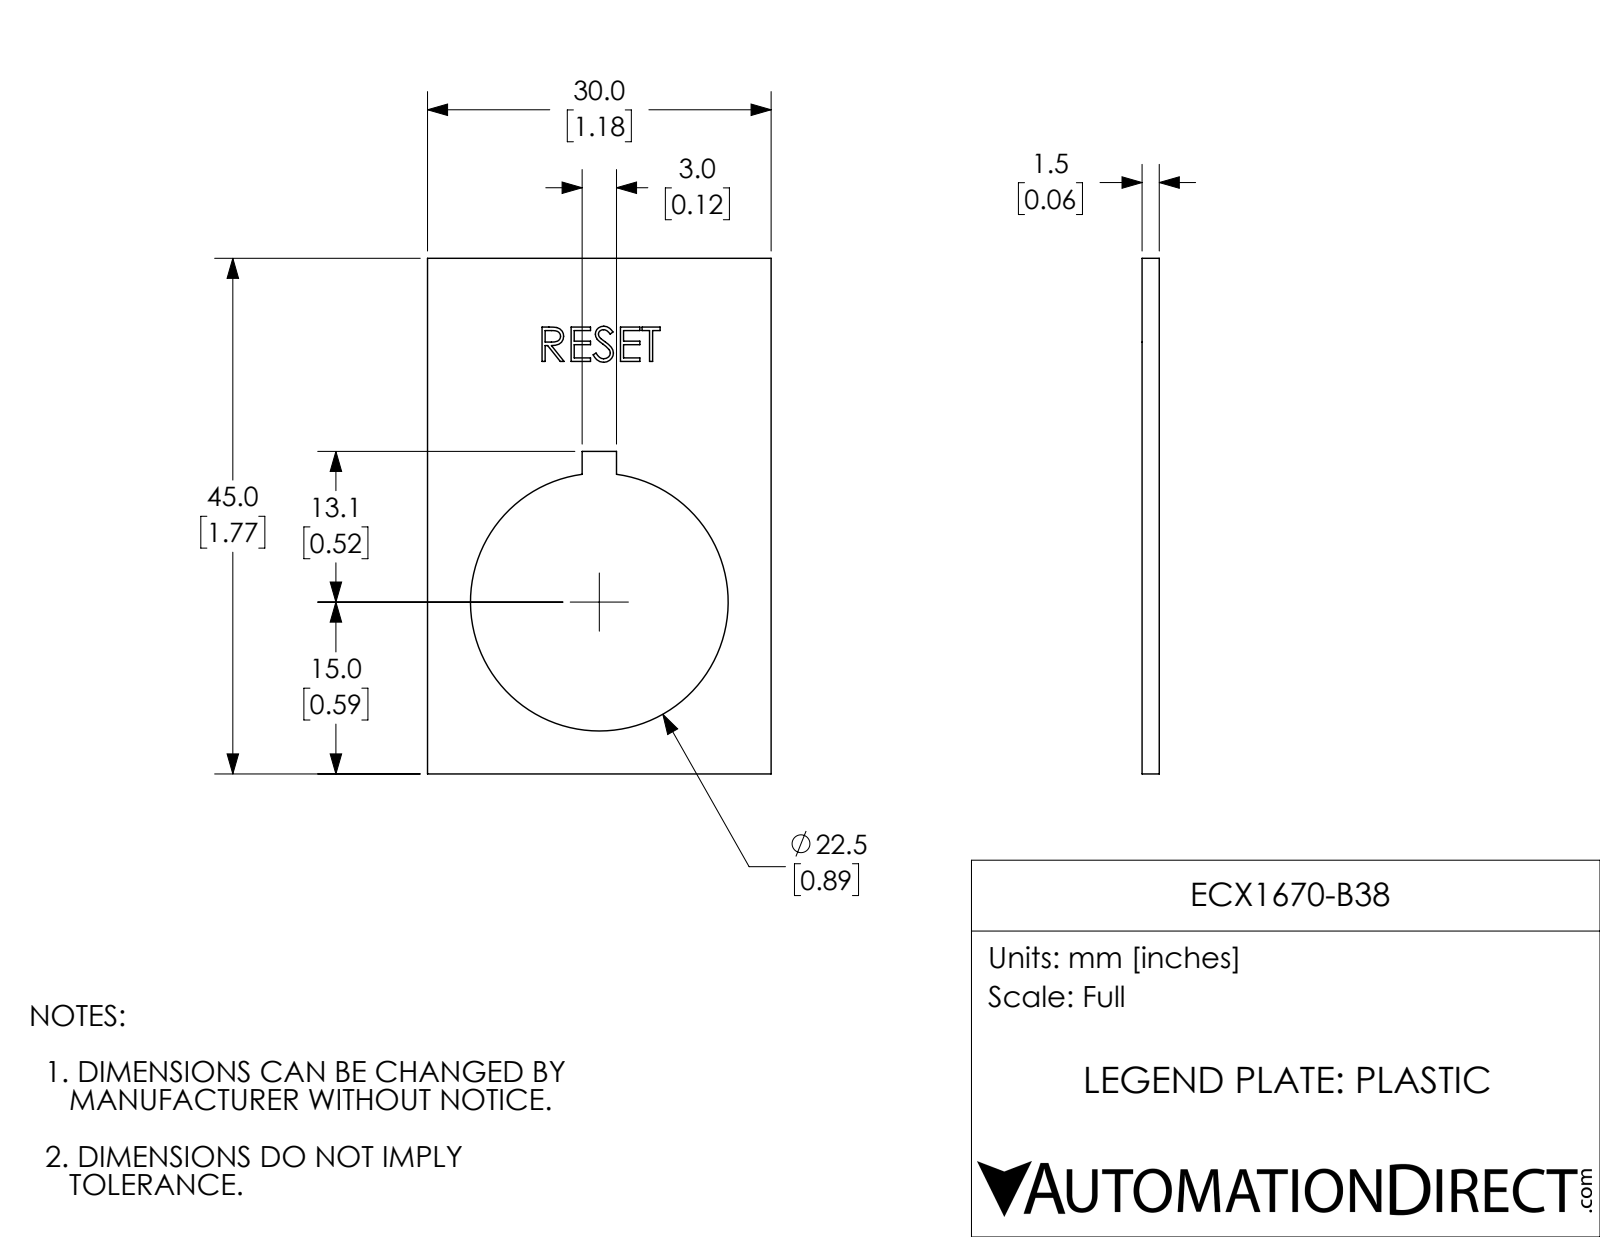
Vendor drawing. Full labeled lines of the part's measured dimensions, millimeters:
Part name (STEP PRODUCT): ECX1670-B38
STEP written by: SolidWorks 2017 (AUTOMOTIVE_DESIGN)
Units: millimetres
Bodies: 1 solid, 83 faces (60 planar, 3 cylindrical, 20 other)
Overall size (bounding box): 45 × 30 × 1.5
Volume: 1 400 mm³ · Surface area: 2 232 mm²
Round holes (diameter × count): ⌀22.5 ×1
Main face-to-face distances: 1.5, 30, 45, 1.5, 13.5, 16.5, 16.8, 28.1, 3, 0.3
